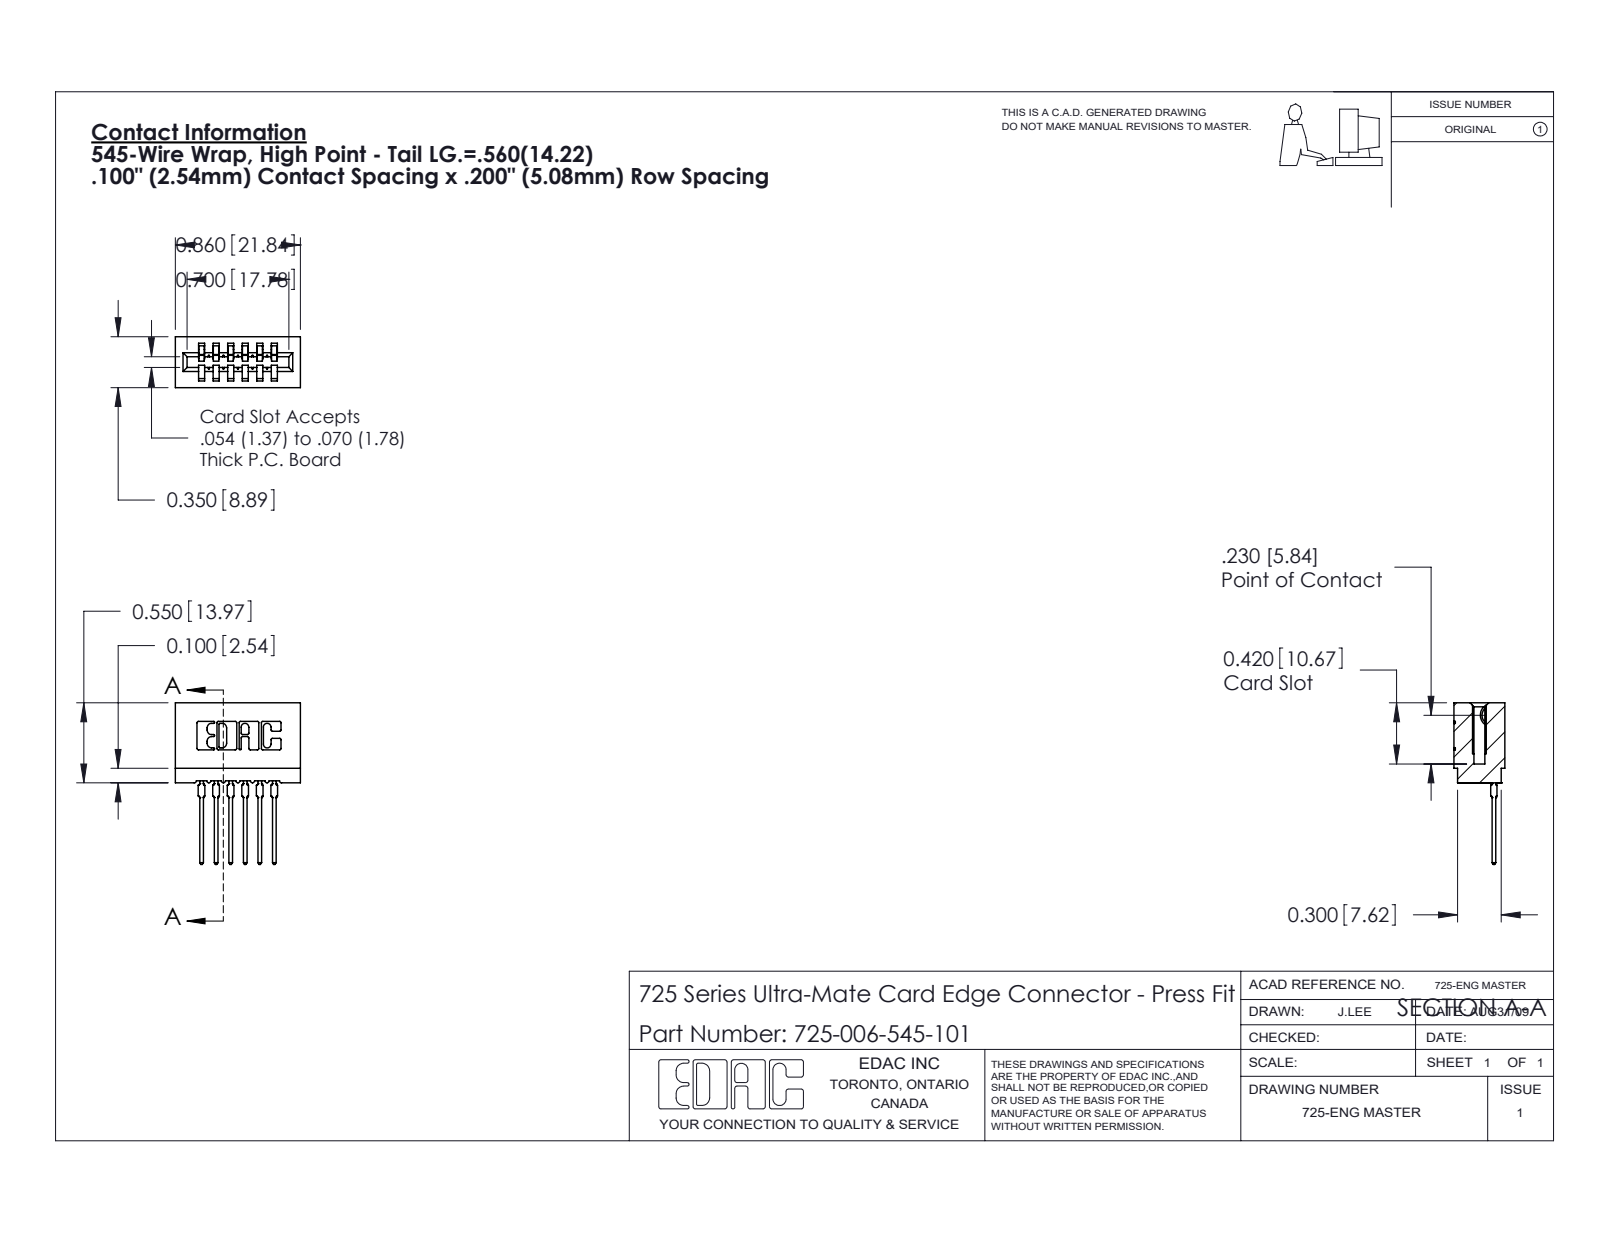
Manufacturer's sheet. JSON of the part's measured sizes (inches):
{"part_name": "725 Part_Insulator Option - 01; 745-292-001_545; 725-006-545-101", "step_written_by": "SolidWorks 2020 (CONFIG_CONTROL_DESIGN)", "units": "inches", "bodies": {"solids": 7, "faces": 767, "planar": 457, "cylindrical": 154, "other": 156}, "overall_size": [1.111, 0.86, 0.35], "volume_in3": 0.114, "surface_area_in2": 4.722, "partial_cylinders_radius": [[0.01, 22], [0.015, 12], [0.021, 12], [0.007, 6], [0.031, 6], [0.005, 4], [0.011, 4], [0.026, 3]], "face_to_face_distances": [0.1, 0.2, 0.3, 0.042, 0.142, 0.058, 0.4, 0.242, 0.158, 0.35]}
